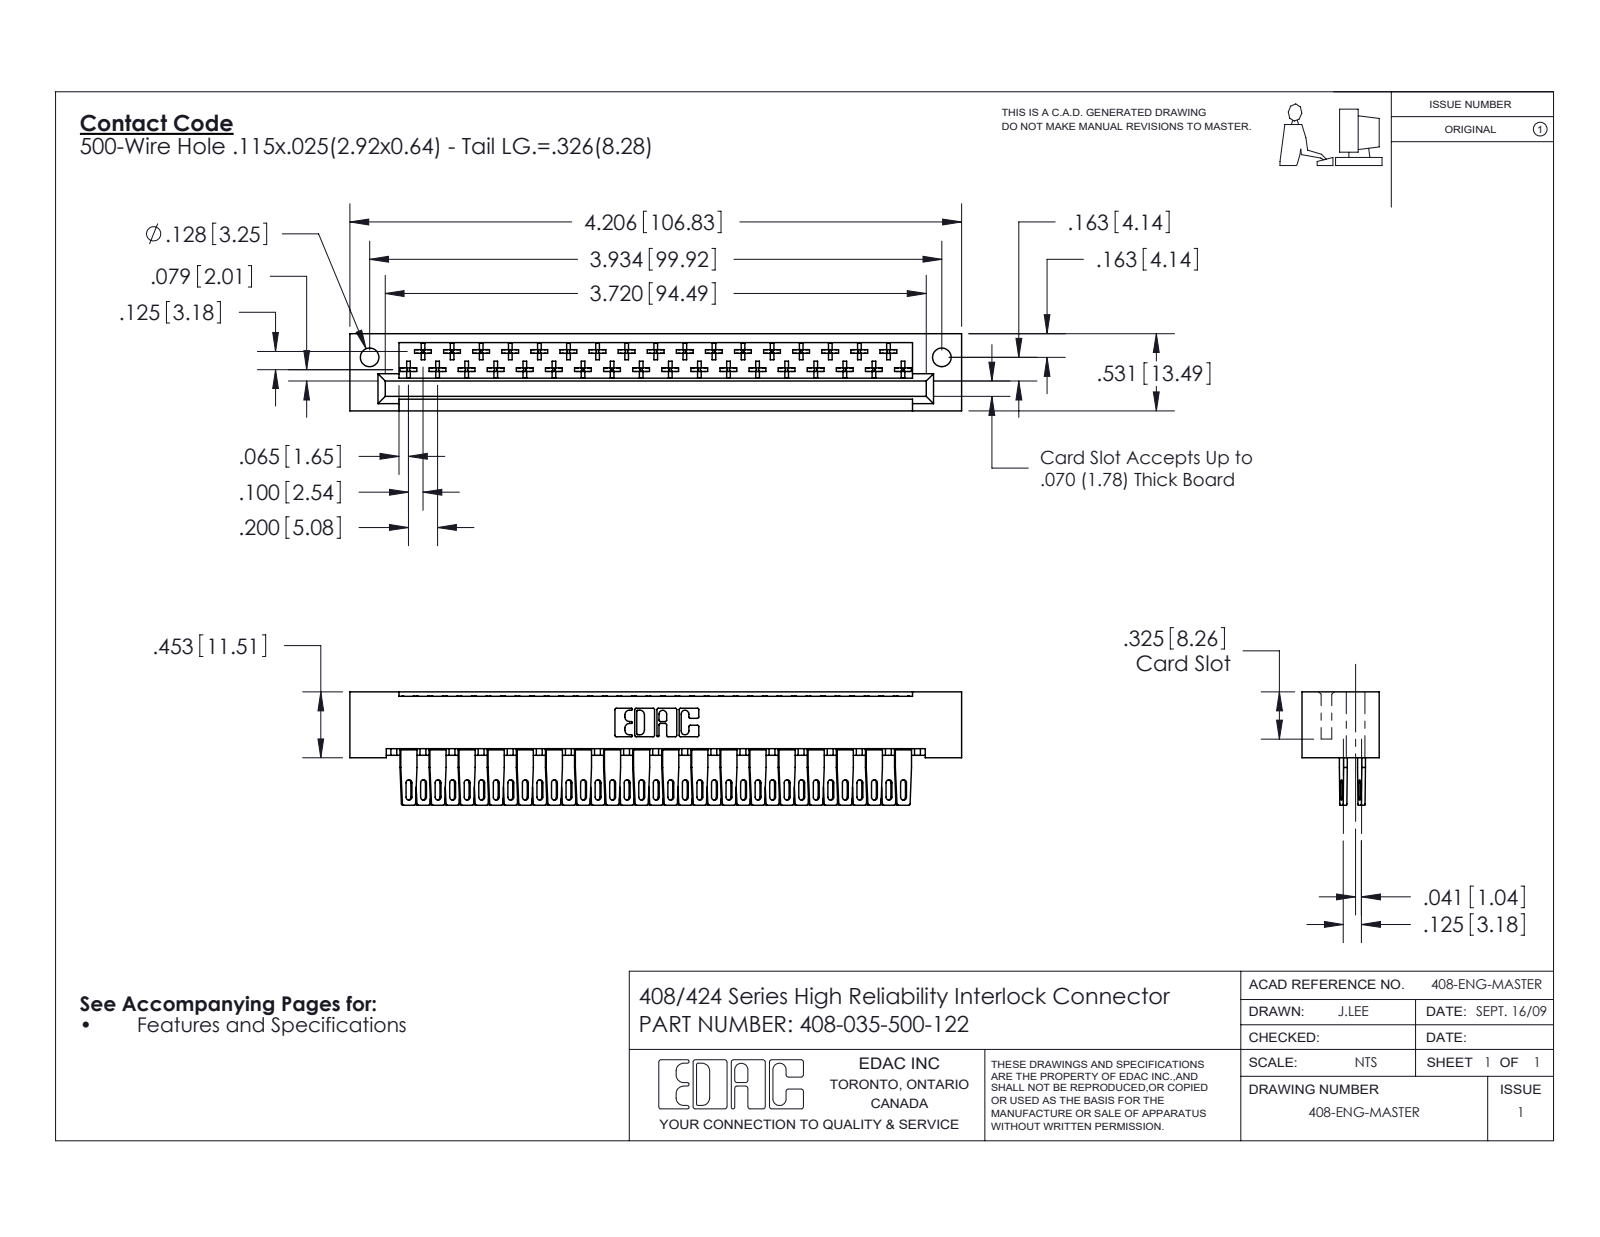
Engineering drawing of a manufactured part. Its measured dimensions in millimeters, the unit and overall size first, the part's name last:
Units: millimetres
Overall size (bounding box): 106.8 × 19.8 × 13.5
Round holes (diameter × count): ⌀3.3 ×2
Partial cylindrical surfaces — rounded edges, fillets, slot ends (radius × count): R0.3 ×280, R0.5 ×70, R0.5 ×37, R0.3 ×22, R0.2 ×6, R0.8 ×6, R0.7 ×3
Main face-to-face distances: 2.5, 7.5, 13.5, 0.6, 3.2, 0.6, 6, 6.6, 6.9, 3.4
Hole centre spacings: 99.9
Volume: 12 000 mm³ · Surface area: 15 860 mm²
Bodies: 36 solids, 2122 faces (1514 planar, 468 cylindrical, 140 other)
Part name (STEP PRODUCT): 408-290-001_408-290-100; 408 Part_035 - 1; 408-035-500-122
STEP written by: SolidWorks 2016 (CONFIG_CONTROL_DESIGN)
